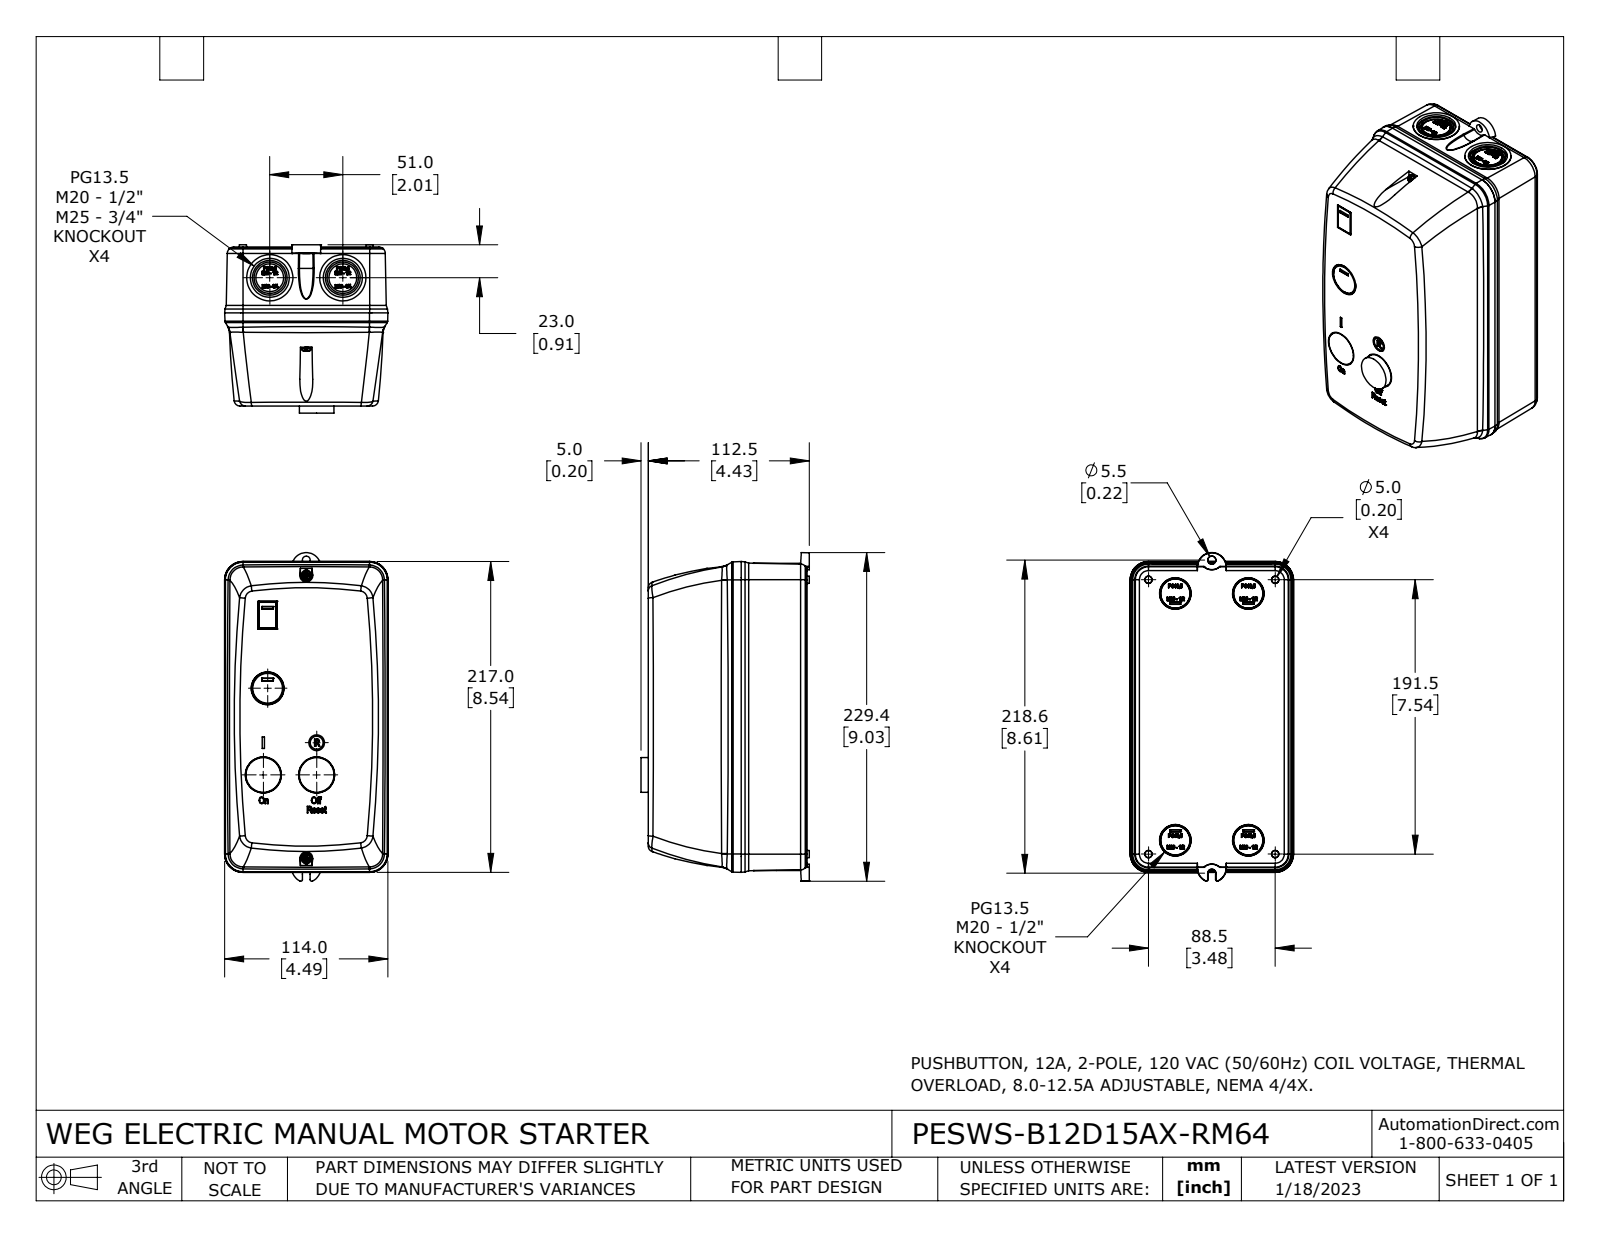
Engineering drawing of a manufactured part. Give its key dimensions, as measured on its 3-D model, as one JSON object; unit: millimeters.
{"part_name": "PESWS-B12D15AX-RM64", "step_written_by": "SolidWorks 2021 (CONFIG_CONTROL_DESIGN)", "units": "millimeters", "bodies": {"solids": 6, "faces": 2195, "planar": 1110, "cylindrical": 92, "other": 993}, "overall_size": [229.44, 117.5, 114.01], "volume_mm3": 2457000, "surface_area_mm2": 166196, "round_holes": [[4.4, 2], [21.91, 2], [27.24, 2], [5.5, 1], [11, 1]], "round_bosses_or_shafts": [[32.26, 2], [24.25, 2], [24.2, 2], [19.37, 2], [7, 2], [3, 2], [9, 1]], "partial_cylinders_radius": [[2, 4], [4.61, 4], [9.54, 4], [6.54, 2], [7.54, 2], [2.08, 1], [2.17, 1], [2.75, 1]], "face_to_face_distances": [46, 65, 111, 0.5, 110.5, 45.5, 110, 1, 109.5, 64], "hole_center_spacings": [10.5, 51, 81.32, 117.22, 127.71, 198, 208.5]}
